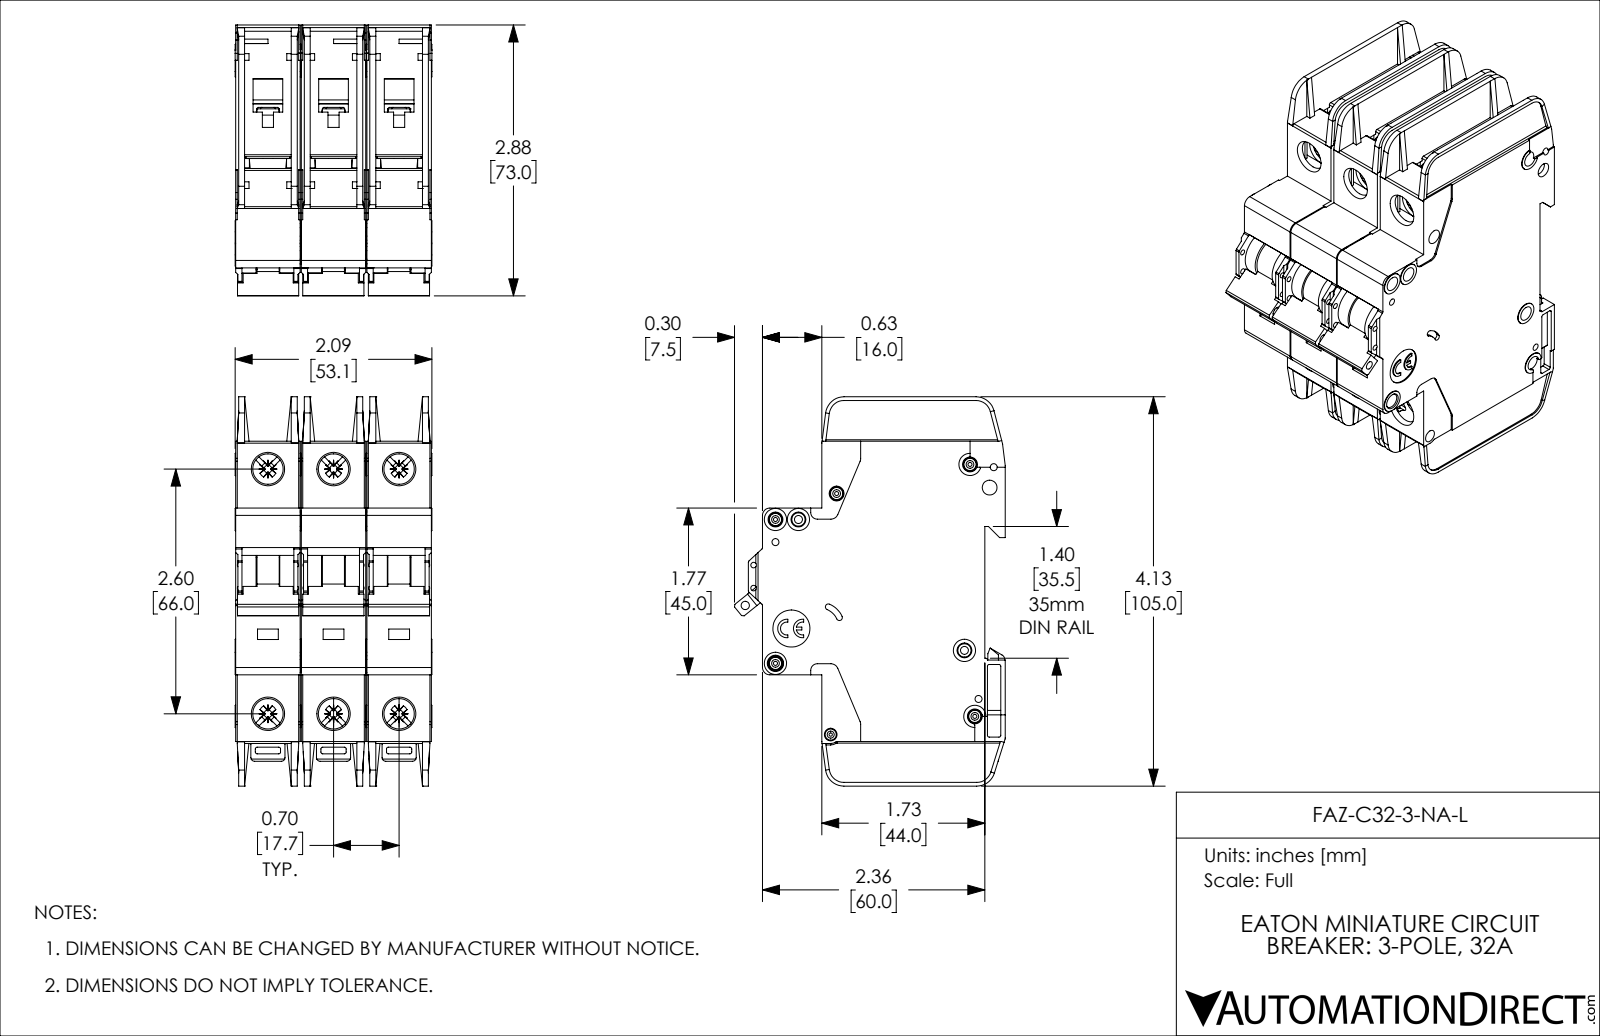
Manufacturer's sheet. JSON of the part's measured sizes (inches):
{"part_name": "FAZ-C32-3-NA-L", "step_written_by": "SolidWorks 2019 (AUTOMOTIVE_DESIGN)", "units": "inches", "bodies": {"solids": 3, "faces": 3381, "planar": 2013, "cylindrical": 1071, "other": 297}, "overall_size": [4.134, 2.876, 2.091], "volume_in3": 14.05, "surface_area_in2": 123, "round_holes": [[0.157, 8], [0.323, 6], [0.043, 5], [0.075, 4], [0.059, 2], [0.085, 2], [0.035, 1], [0.089, 1], [0.098, 1], [0.134, 1], [0.394, 1]], "round_bosses_or_shafts": [[0.13, 5], [0.236, 4], [0.118, 4], [0.098, 3]], "partial_cylinders_radius": [[0.02, 72], [0.016, 30], [0.039, 18], [0.043, 12], [0.079, 12], [0.008, 6], [0.01, 6], [0.028, 6]], "face_to_face_distances": [0.697, 0.047, 1.394, 0.685, 0.591, 1.382, 0.744, 0.65, 0.106, 0.094], "hole_center_spacings": [0.697, 2.69, 2.598, 0.244, 0.537, 0.87, 1.394, 2.948]}
